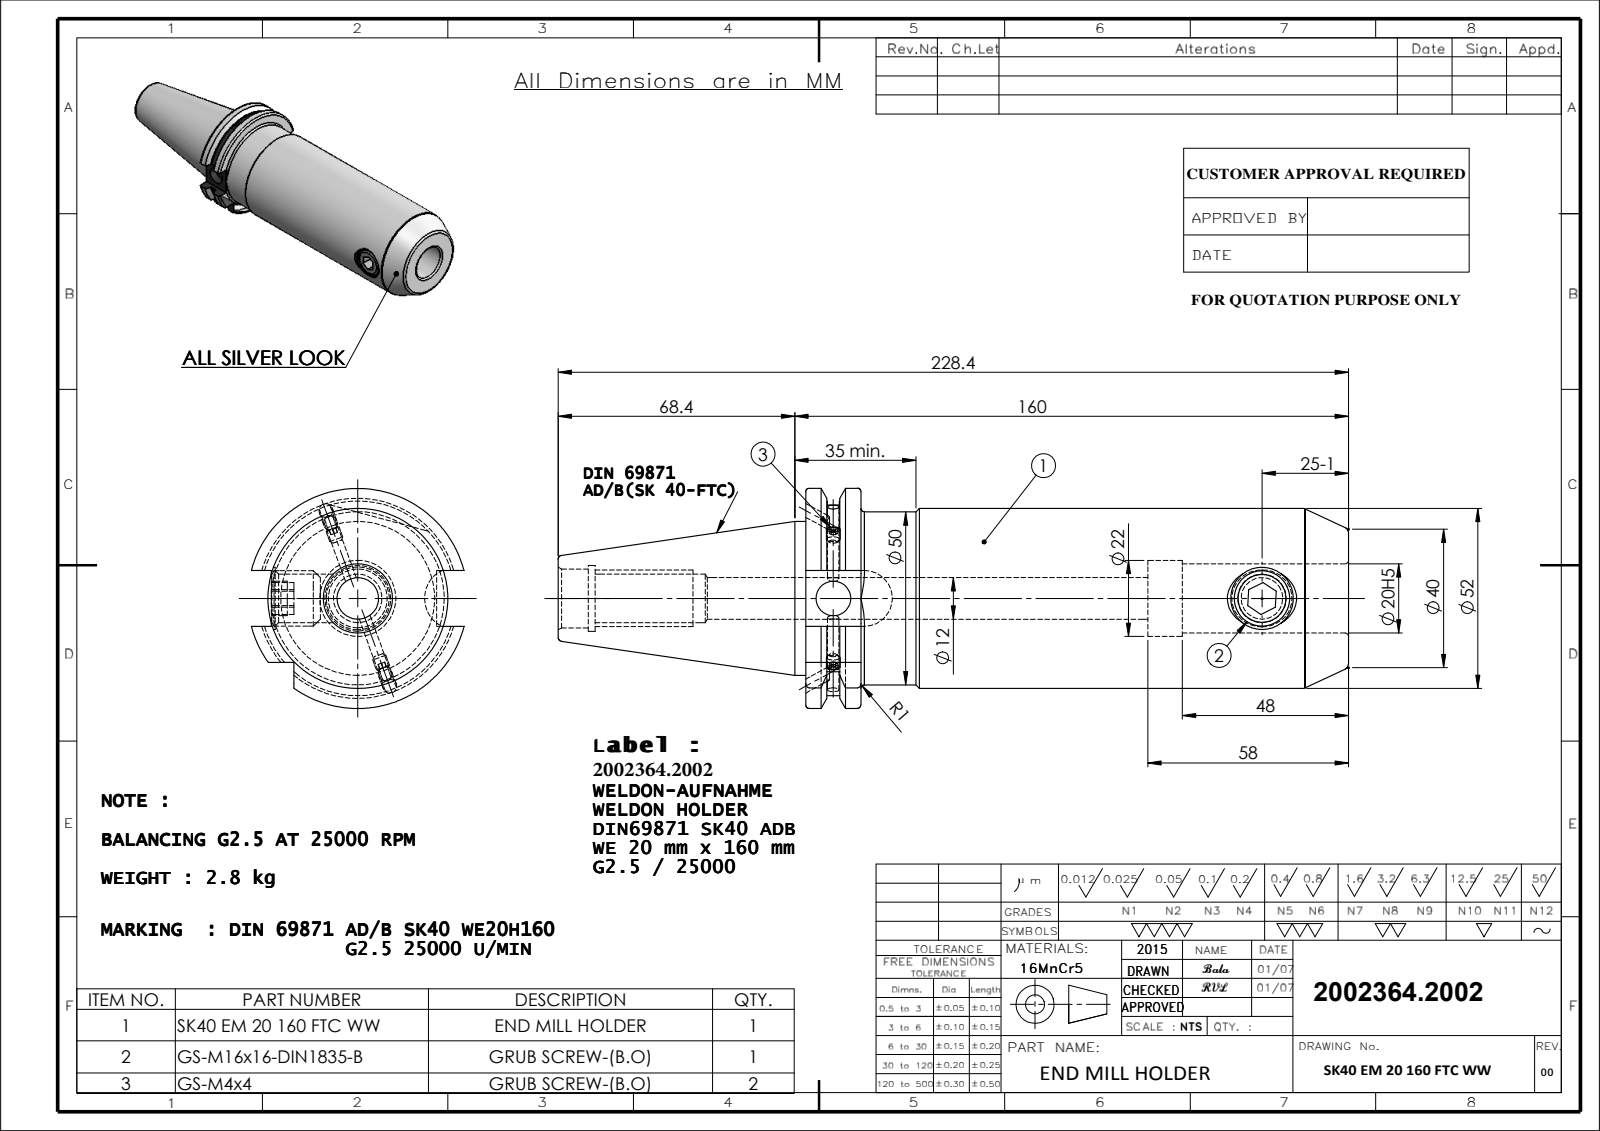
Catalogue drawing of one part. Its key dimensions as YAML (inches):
part_name: "91406-WE720160; M16X16_ISO 4026 - M16 x 10-N; SK40 EM 20 160 FTC WW; Copy of M4X4_DIN 913 - M4 x 4-N"
step_written_by: "SolidWorks 2009 (CONFIG_CONTROL_DESIGN)"
units: inches
bodies: {solids: 4, faces: 167, planar: 59, cylindrical: 47, other: 61}
overall_size: [8.992, 2.502, 2.42]
volume: 22.05
surface_area: 80.69
round_holes:
  - {diameter: 0.551, count: 2}
  - {diameter: 0.13, count: 1}
  - {diameter: 0.394, count: 1}
  - {diameter: 0.472, count: 1}
  - {diameter: 0.669, count: 1}
  - {diameter: 0.709, count: 1}
  - {diameter: 0.748, count: 1}
  - {diameter: 0.787, count: 1}
  - {diameter: 0.866, count: 1}
round_bosses_or_shafts:
  - {diameter: 0.157, count: 2}
  - {diameter: 2.047, count: 1}
  - {diameter: 1.969, count: 1}
  - {diameter: 1.75, count: 1}
  - {diameter: 0.63, count: 1}
partial_cylinders:
  - {radius: 0.317, count: 1}
  - {radius: 1.107, count: 1}
  - {radius: 1.251, count: 1}
face_to_face_distances: [6.173, 0.626, 5.547, 3.89, 3.264, 2.283, 0.634, 1.882, 2.819, 3.445]
hole_center_spacings: [4.876]
